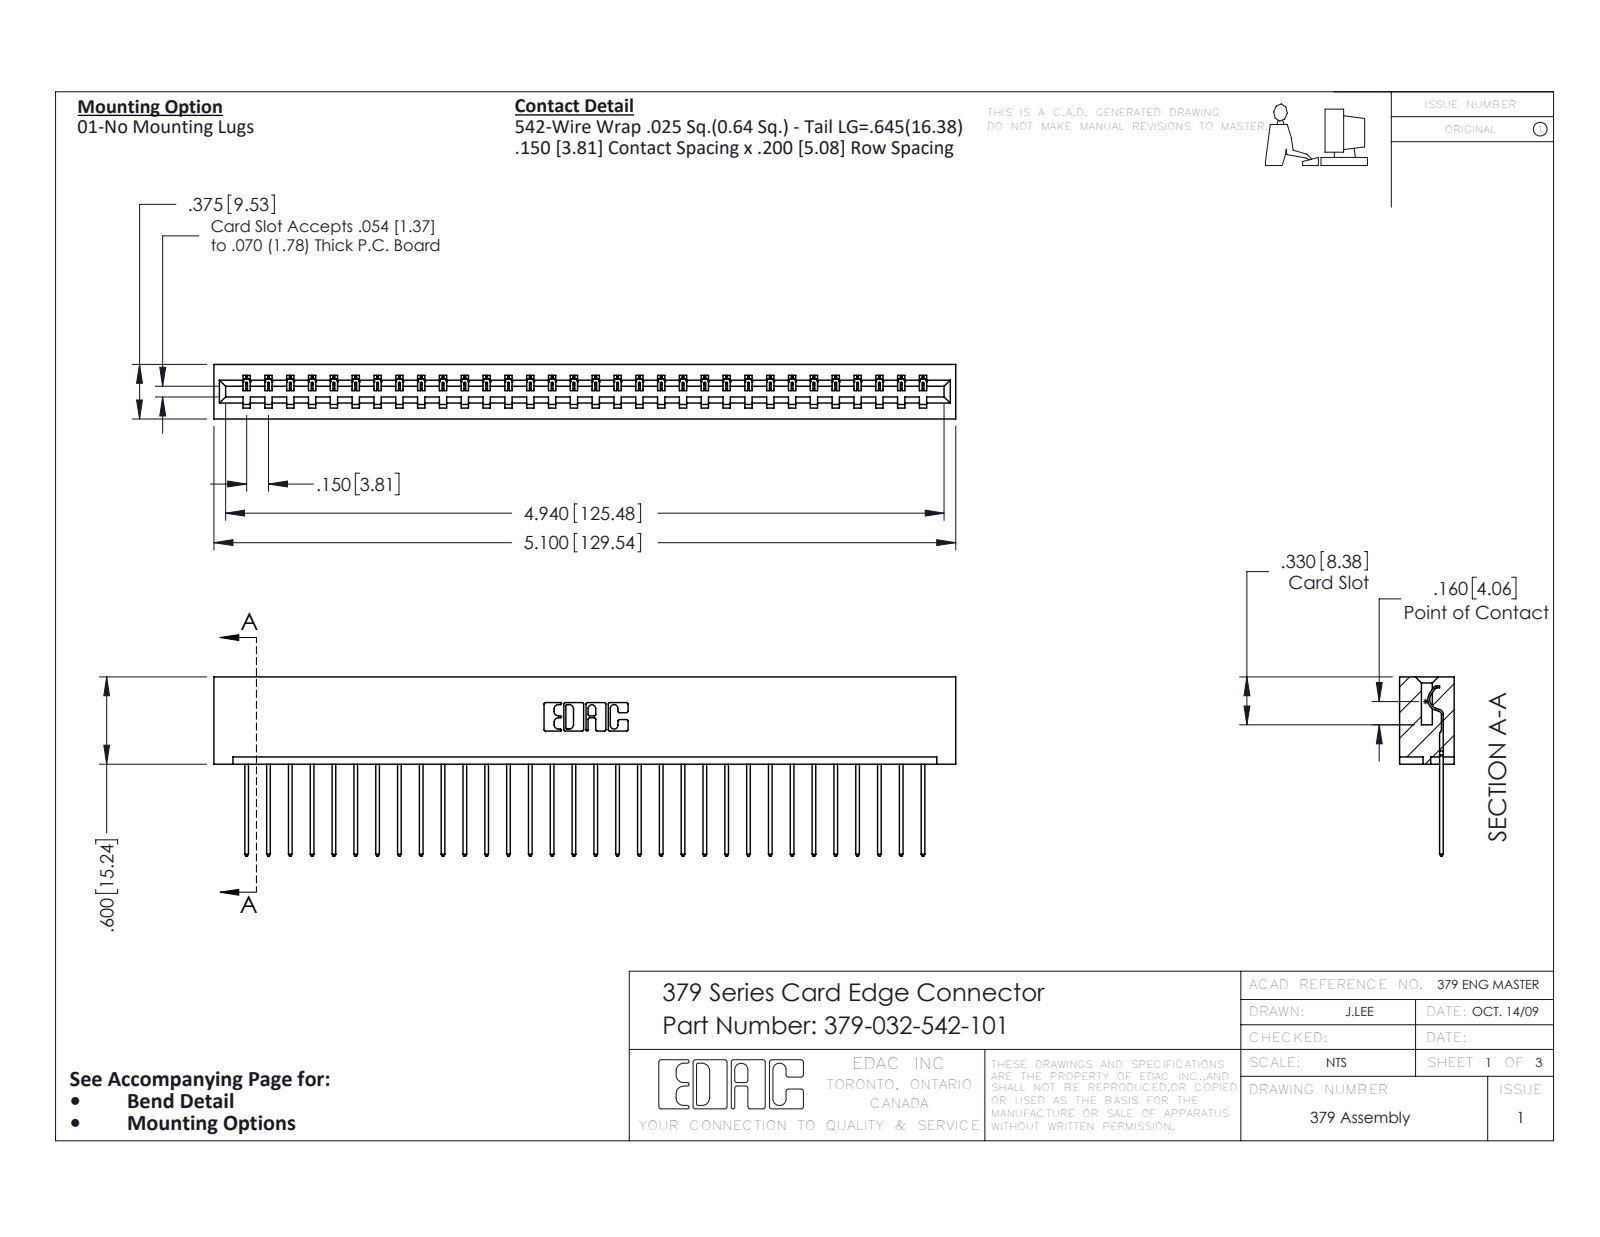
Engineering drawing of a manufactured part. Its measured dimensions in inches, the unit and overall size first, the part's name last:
Units: inches
Overall size (bounding box): 5.1 × 1.232 × 0.375
Partial cylindrical surfaces — rounded edges, fillets, slot ends (radius × count): R0.006 ×64, R0.01 ×64, R0.01 ×22, R0.007 ×6, R0.031 ×6, R0.026 ×3, R0.014 ×1, R0.022 ×1
Main face-to-face distances: 0.3, 0.075, 0.375, 0.225, 0.1, 0.275, 0.025, 0.6, 0.2, 0.15
Volume: 0.871 in³ · Surface area: 23.25 in²
Bodies: 33 solids, 1962 faces (1410 planar, 552 cylindrical, 0 other)
Part name (STEP PRODUCT): 345-292-001_345-293-142; 379 Part_Lugless; 379-032-542-101
STEP written by: SolidWorks 2016 (CONFIG_CONTROL_DESIGN)
